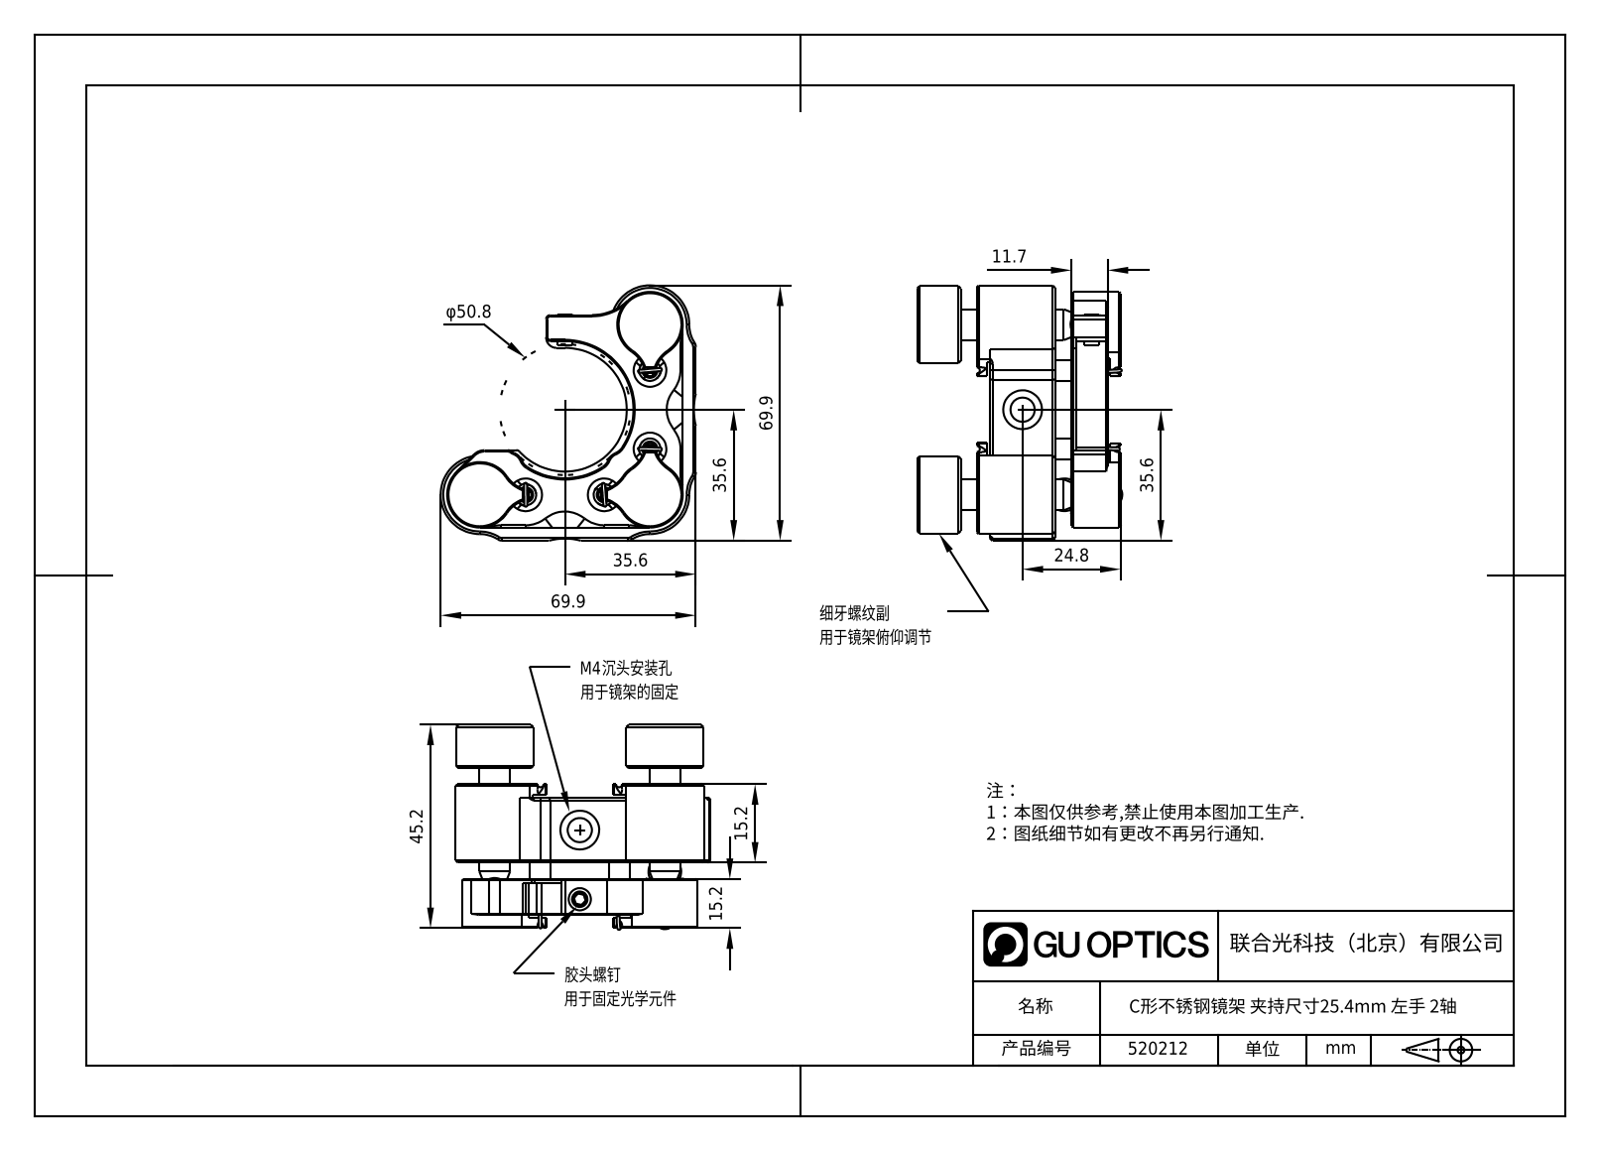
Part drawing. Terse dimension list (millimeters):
name: 30.8.8-14，M4尼龙头顶丝，A_30.8.8-LNJ4*4; 1.1.19.55-ZJD-K2.0-2R; DXVS，真空型M6x0.25六角调节器，零部件，Rev.A_3.2.11.2.1-DXVS-0625-26.6; 36.1，440c不锈钢滚珠_36.1.6_GZ-B4 (+3 more)
written by: SolidWorks 2021 (CONFIG_CONTROL_DESIGN)
unit: mm
bodies: 21 solids, 727 faces (196 planar, 187 cylindrical, 344 other)
size: 69.85 × 69.85 × 45.24
volume: 37 800 mm³; area: 22 520 mm²
holes: 6× ⌀6.35, 4× ⌀4.7, 4× ⌀7.54, 2× ⌀1.8, 2× ⌀2.01, 2× ⌀3.3, 2× ⌀3.99, 2× ⌀4, 2× ⌀6, 2× ⌀7
bosses: 8× ⌀4, 2× ⌀15.24, 2× ⌀15, 2× ⌀5, 2× ⌀3
rounds: 19× R6.48, 8× R3.17, 5× R3, 4× R1, 4× R4, 4× R64.14, 3× R0.6, 3× R6.35
face distances: 12.7, 15.88, 2.54, 3.18, 15.24, 18.42, 31.12, 28.58, 33.66, 26.82
hole spacings: 9.5, 43.9, 54.17, 69.08, 5, 5.01, 5.5, 9.44
